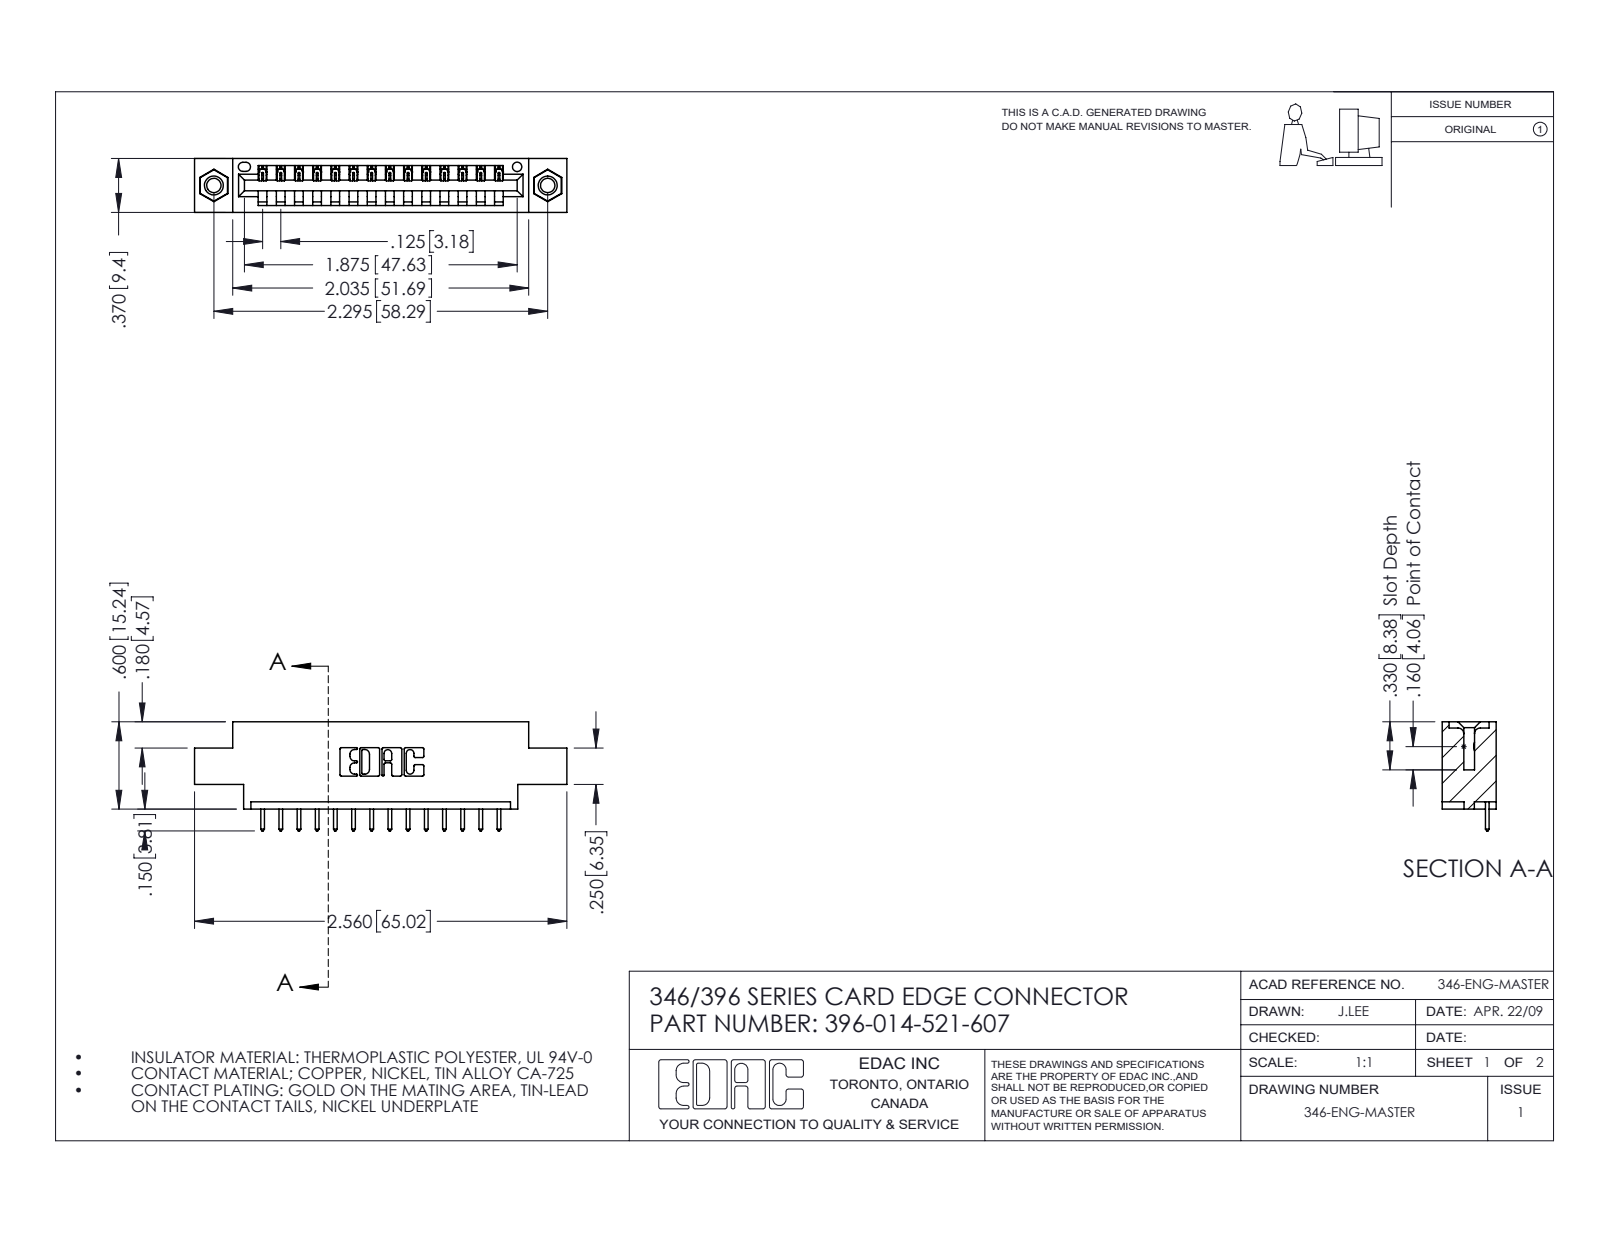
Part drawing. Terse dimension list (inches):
name: 345-250-001_345-250-005-103; 396-014-521-607; 346 Part_0.170 Offset - 0.156 Dia-TI; 345-292-001_345-293-121
written by: SolidWorks 2016 (CONFIG_CONTROL_DESIGN)
unit: in
bodies: 17 solids, 998 faces (672 planar, 310 cylindrical, 16 other)
size: 2.56 × 0.75 × 0.37
volume: 0.355 in³; area: 10.87 in²
holes: 2× ⌀0.098, 2× ⌀0.125, 2× ⌀0.156, 1× ⌀0.064
bosses: 2× ⌀0.155
rounds: 28× R0.006, 28× R0.01, 22× R0.01, 6× R0.007, 6× R0.031, 3× R0.026, 2× R0.031, 2× R0.04
face distances: 0.37, 0.048, 0.322, 0.25, 0.222, 0.148, 0.072, 0.298, 0.025, 0.1
hole spacings: 0.246, 2.089, 2.295
